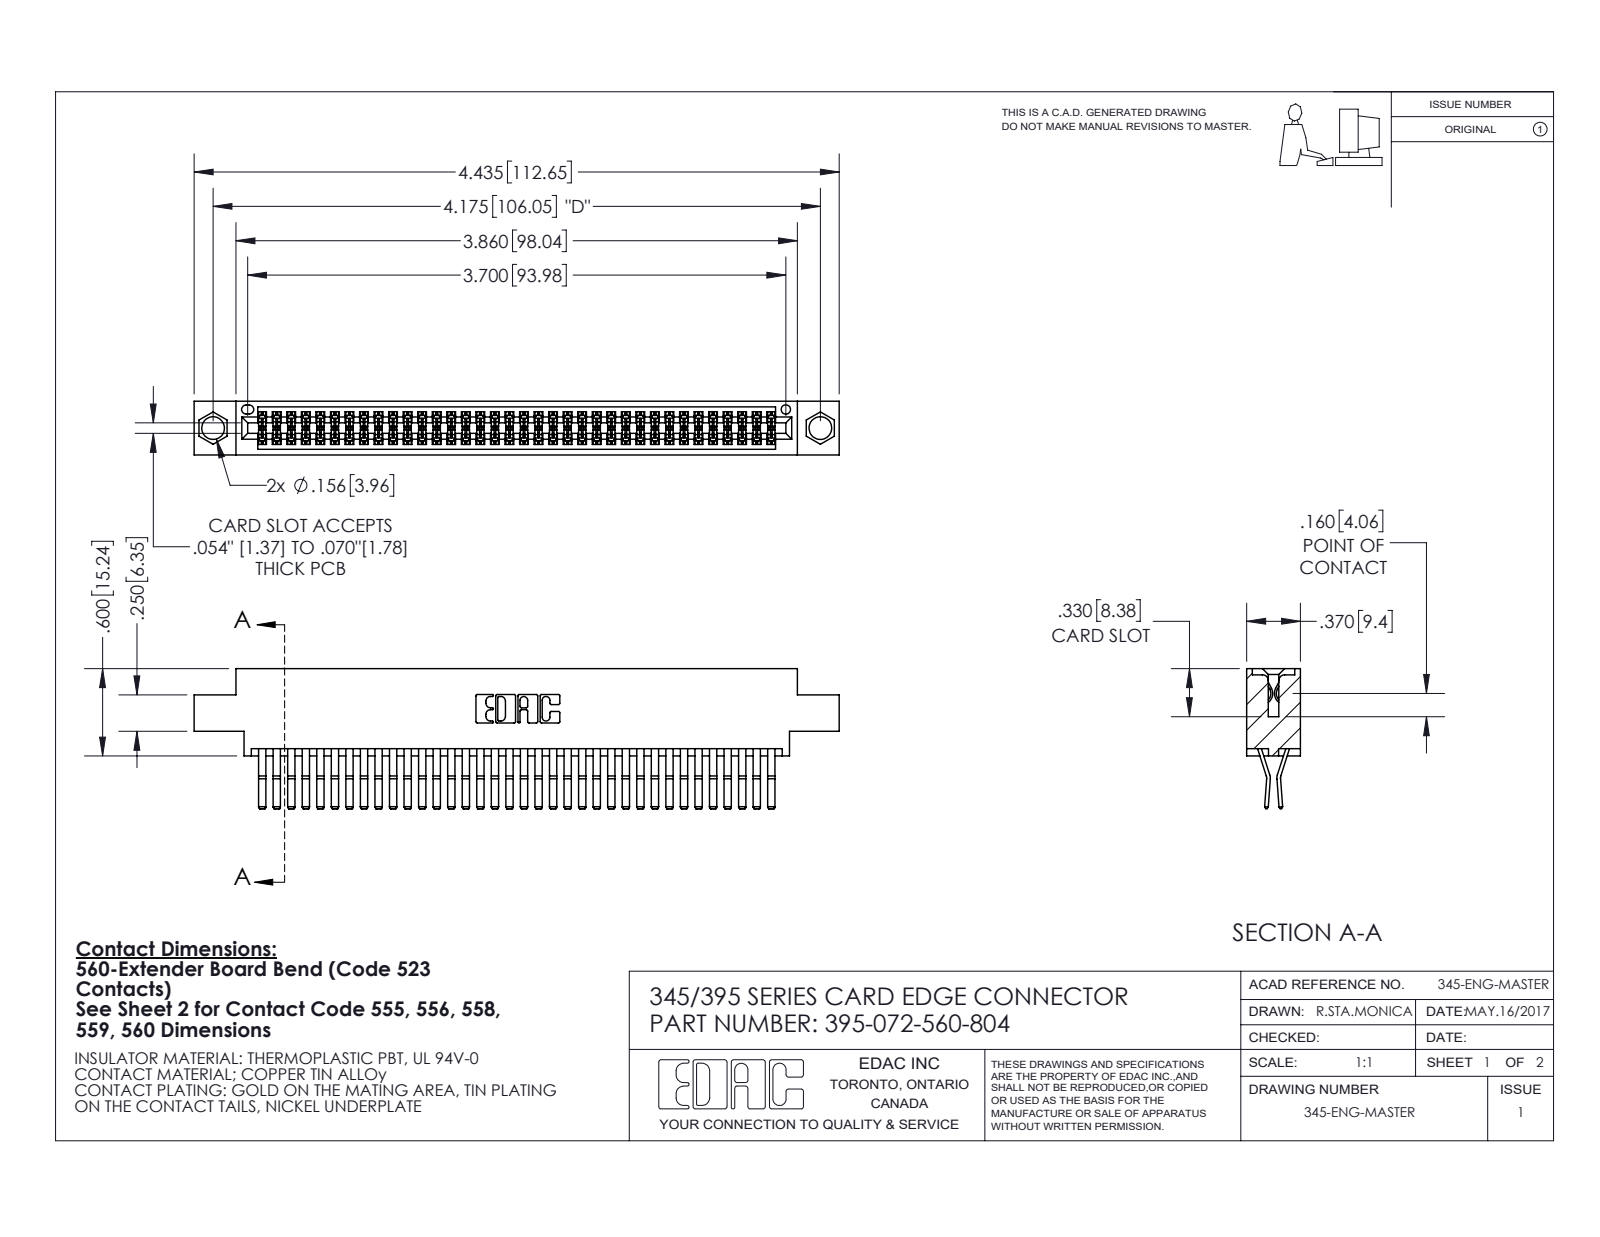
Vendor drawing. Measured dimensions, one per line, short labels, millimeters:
name: 345 Part_0.170 Offset - 0.156 Dia-TI; 345-292-001_560 Tail; 395-072-560-804
written by: SolidWorks 2020 (CONFIG_CONTROL_DESIGN)
unit: mm
bodies: 73 solids, 3888 faces (2474 planar, 1414 cylindrical, 0 other)
size: 112.6 × 24.4 × 9.4
volume: 11 100 mm³; area: 17 560 mm²
holes: 2× ⌀4, 1× ⌀1.6
rounds: 108× R0.2, 22× R0.3, 6× R0.2, 6× R0.8, 3× R0.7, 2× R0.3, 2× R0.4, 2× R0.5
face distances: 0.6, 1.8, 7.6, 9.4, 5.1, 2.5, 6.9, 5.7, 4.4, 3.8
hole spacings: 6.9, 100.1, 106
